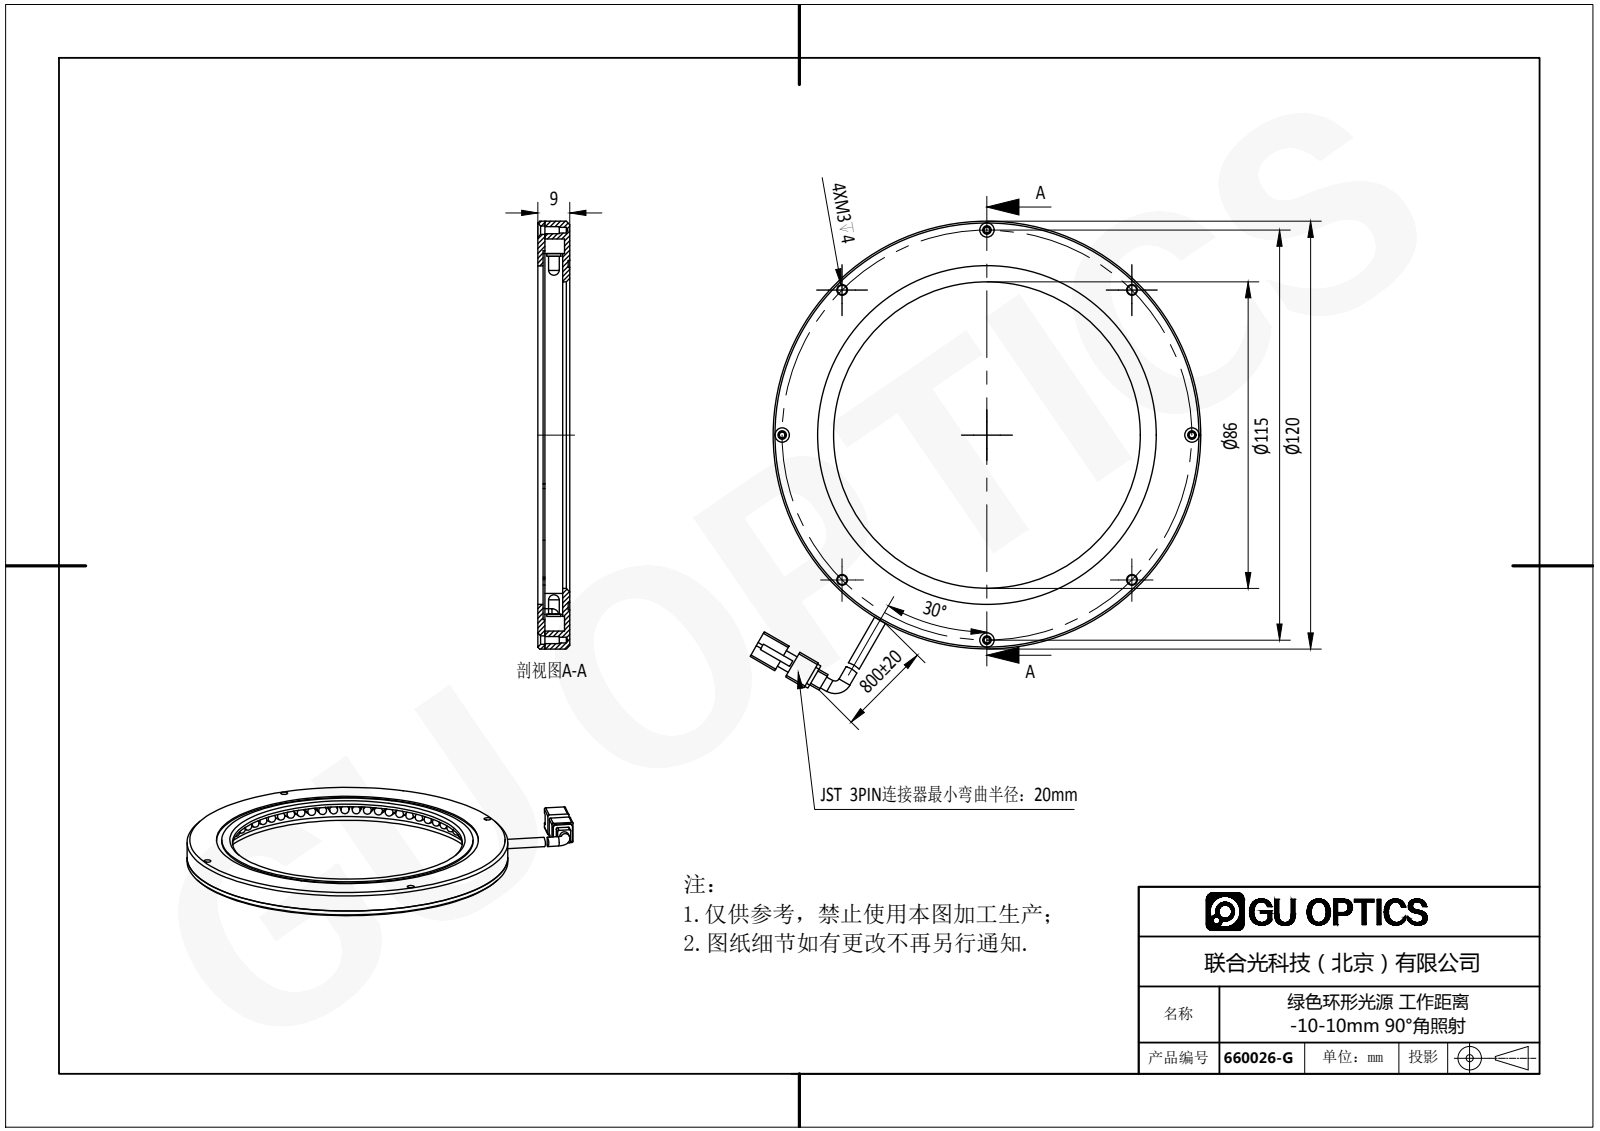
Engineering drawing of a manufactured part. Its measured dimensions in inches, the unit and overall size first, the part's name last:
Units: inches
Overall size (bounding box): 5.218 × 4.978 × 0.437
Round holes (diameter × count): ⌀0.063 ×4, ⌀0.079 ×4, ⌀0.094 ×4, ⌀0.102 ×4, ⌀0.118 ×4, ⌀0.138 ×1, ⌀3.386 ×1, ⌀3.74 ×1, ⌀3.858 ×1, ⌀4.055 ×1, ⌀4.075 ×1, ⌀4.331 ×1
Round bosses / shafts (diameter × count): ⌀0.15 ×69, ⌀0.118 ×69, ⌀0.138 ×2, ⌀4.724 ×1, ⌀4.079 ×1, ⌀4.008 ×1, ⌀3.701 ×1
Partial cylindrical surfaces — rounded edges, fillets, slot ends (radius × count): R0.039 ×12, R0.02 ×8, R0.081 ×2, R0.071 ×1, R0.295 ×1, R2.024 ×1, R2.126 ×1
Main face-to-face distances: 0.276, 0.079, 0.354, 0.02, 0.059, 0.217, 0.295, 0.197, 0.236, 0.039
Hole centre spacings: 1.733, 2.264, 3.202, 4.183, 4.183, 4.528, 1.732, 2.263
Volume: 1.874 in³ · Surface area: 59.39 in²
Bodies: 75 solids, 1433 faces (928 planar, 409 cylindrical, 96 other)
Part name (STEP PRODUCT): 660026-G
STEP written by: SolidWorks 2016 (AUTOMOTIVE_DESIGN)
